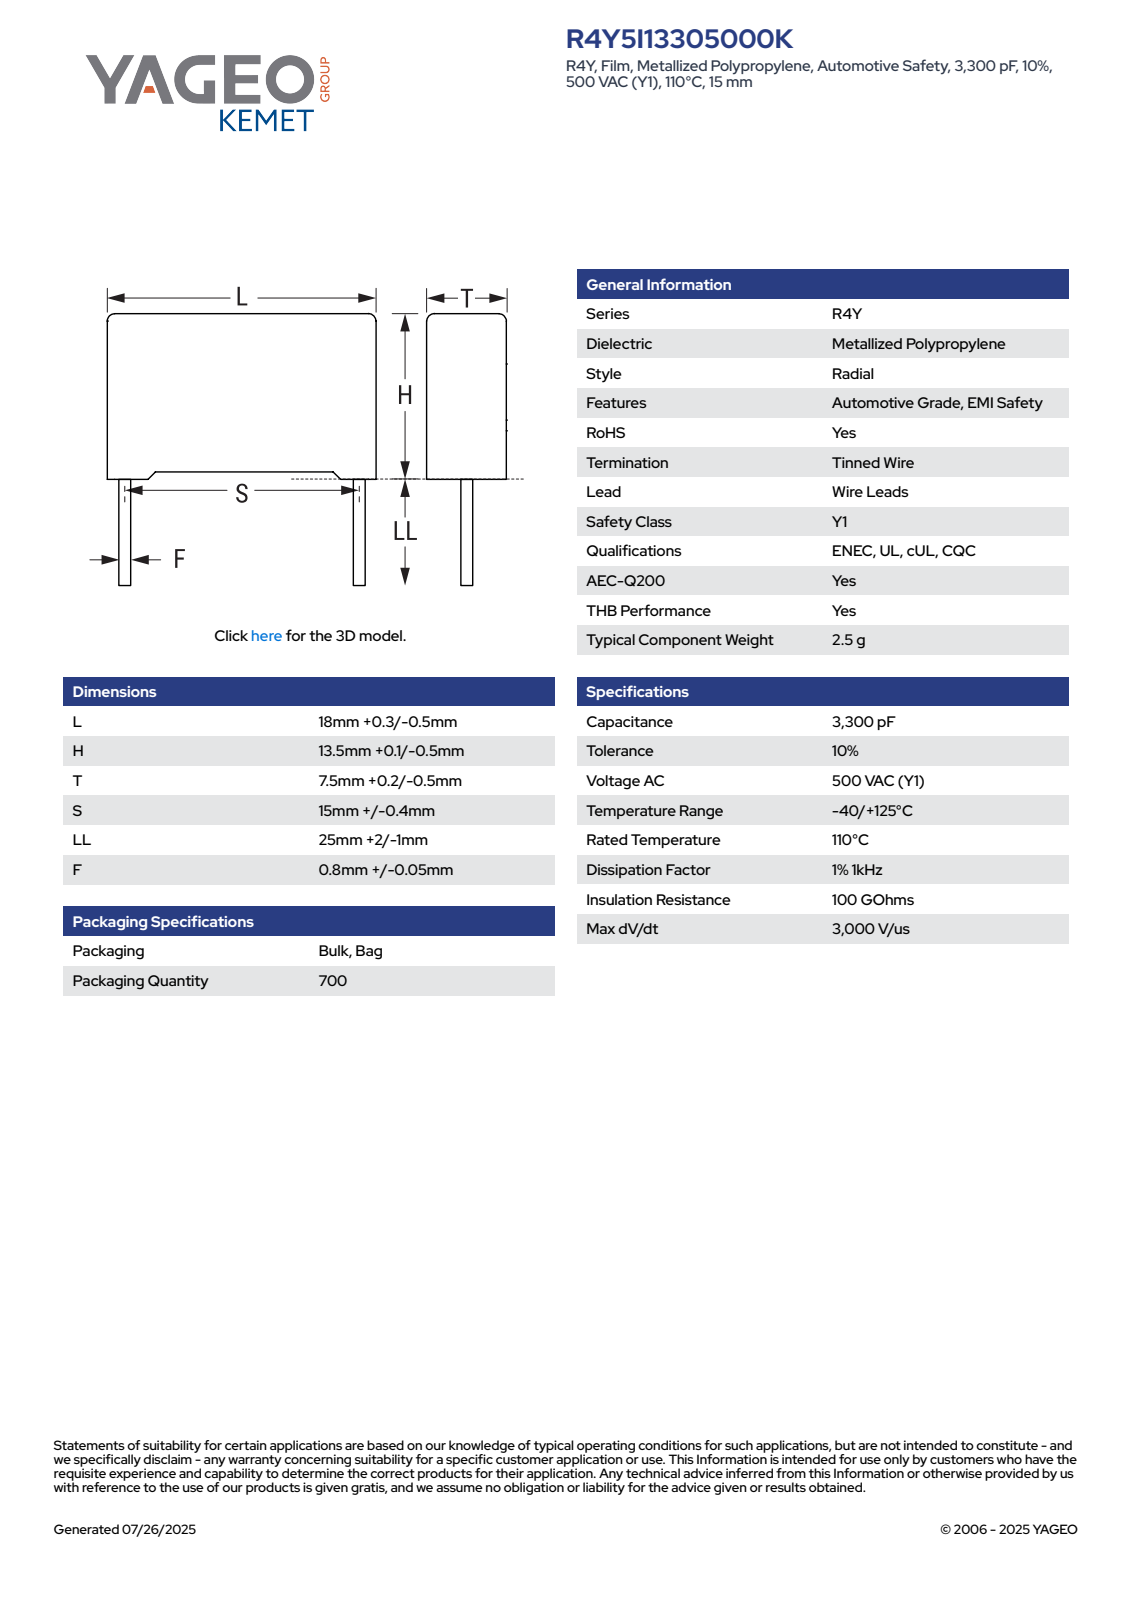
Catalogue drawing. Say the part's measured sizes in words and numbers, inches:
The part is named "CFR_RB2_18X13.5X7.5_L18.3H13.6T7.7S15LL27F0.85". Its 3-D file was written by "SolidWorks 2021 (AUTOMOTIVE_DESIGN)". It is 4 solids with 85 faces: 77 planar, 8 cylindrical and 0 other. Overall it measures 1.598 by 0.72 by 0.304 inches. Its volume is 0.113 cubic inches and its surface area 1.806 square inches. Round bosses or shafts: 2 of diameter 0.033. Partial cylindrical surfaces (rounded edges, fillets, slot ends): 4 of radius 0.02. The main face-to-face distances are 0.303, 0.506, 0.72, 0.024, 0.03, 0.535, 0.279, 0.019, 0.517, 0.696.
